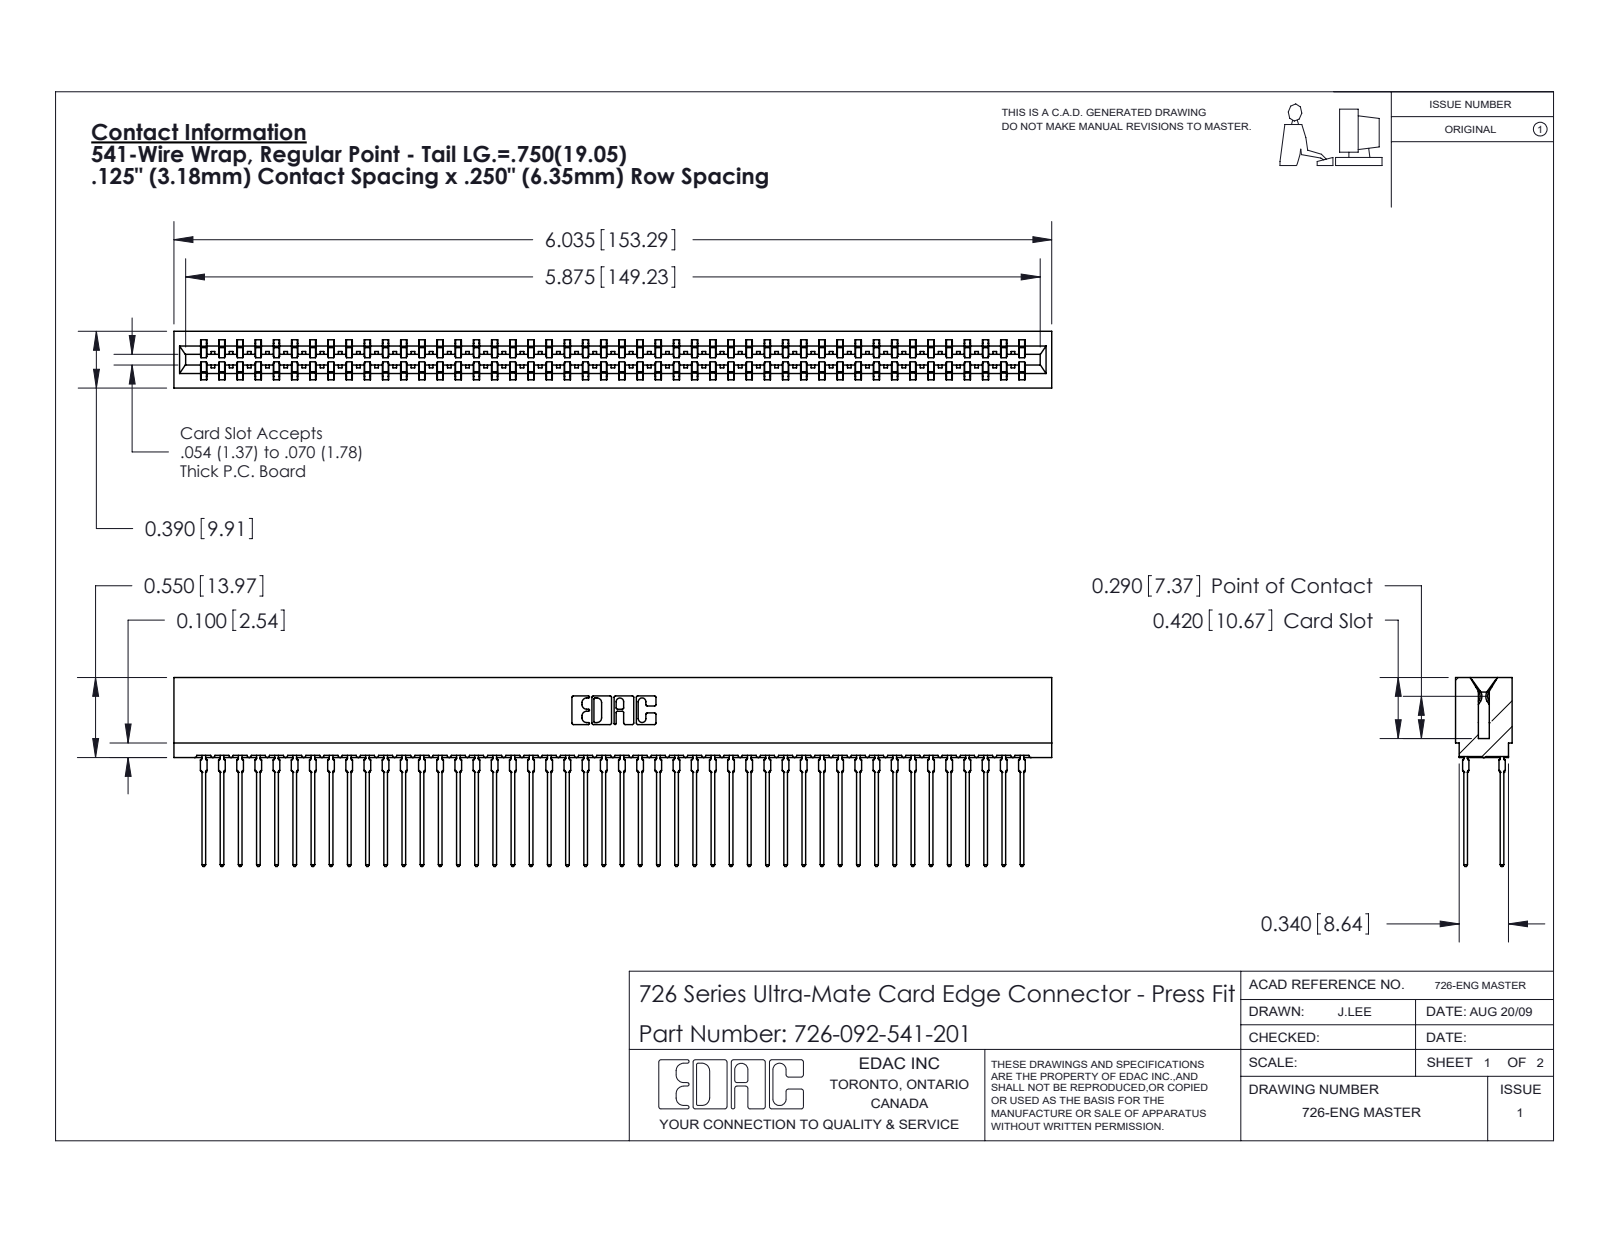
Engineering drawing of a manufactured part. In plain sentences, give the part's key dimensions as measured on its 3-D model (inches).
The part is named "726 Part_.515 Slot Depth - 01; 726-092-541-201; 746-292-001_541". Its 3-D file was written by "SolidWorks 2020 (CONFIG_CONTROL_DESIGN)". It is 93 solids with 8331 faces: 4287 planar, 1652 cylindrical and 2392 other. Overall it measures 6.035 by 1.299 by 0.39 inches. Its volume is 0.89 cubic inches and its surface area 41.44 square inches. Partial cylindrical surfaces (rounded edges, fillets, slot ends): 184 of radius 0.021, 47 of radius 0.015, 22 of radius 0.01, 8 of radius 0.005, 8 of radius 0.011, 6 of radius 0.007, 6 of radius 0.031, 3 of radius 0.026. The main face-to-face distances are 0.057, 0.333, 0.025, 0.307, 0.25, 0.083, 0.39, 0.275, 0.225, 0.365.
